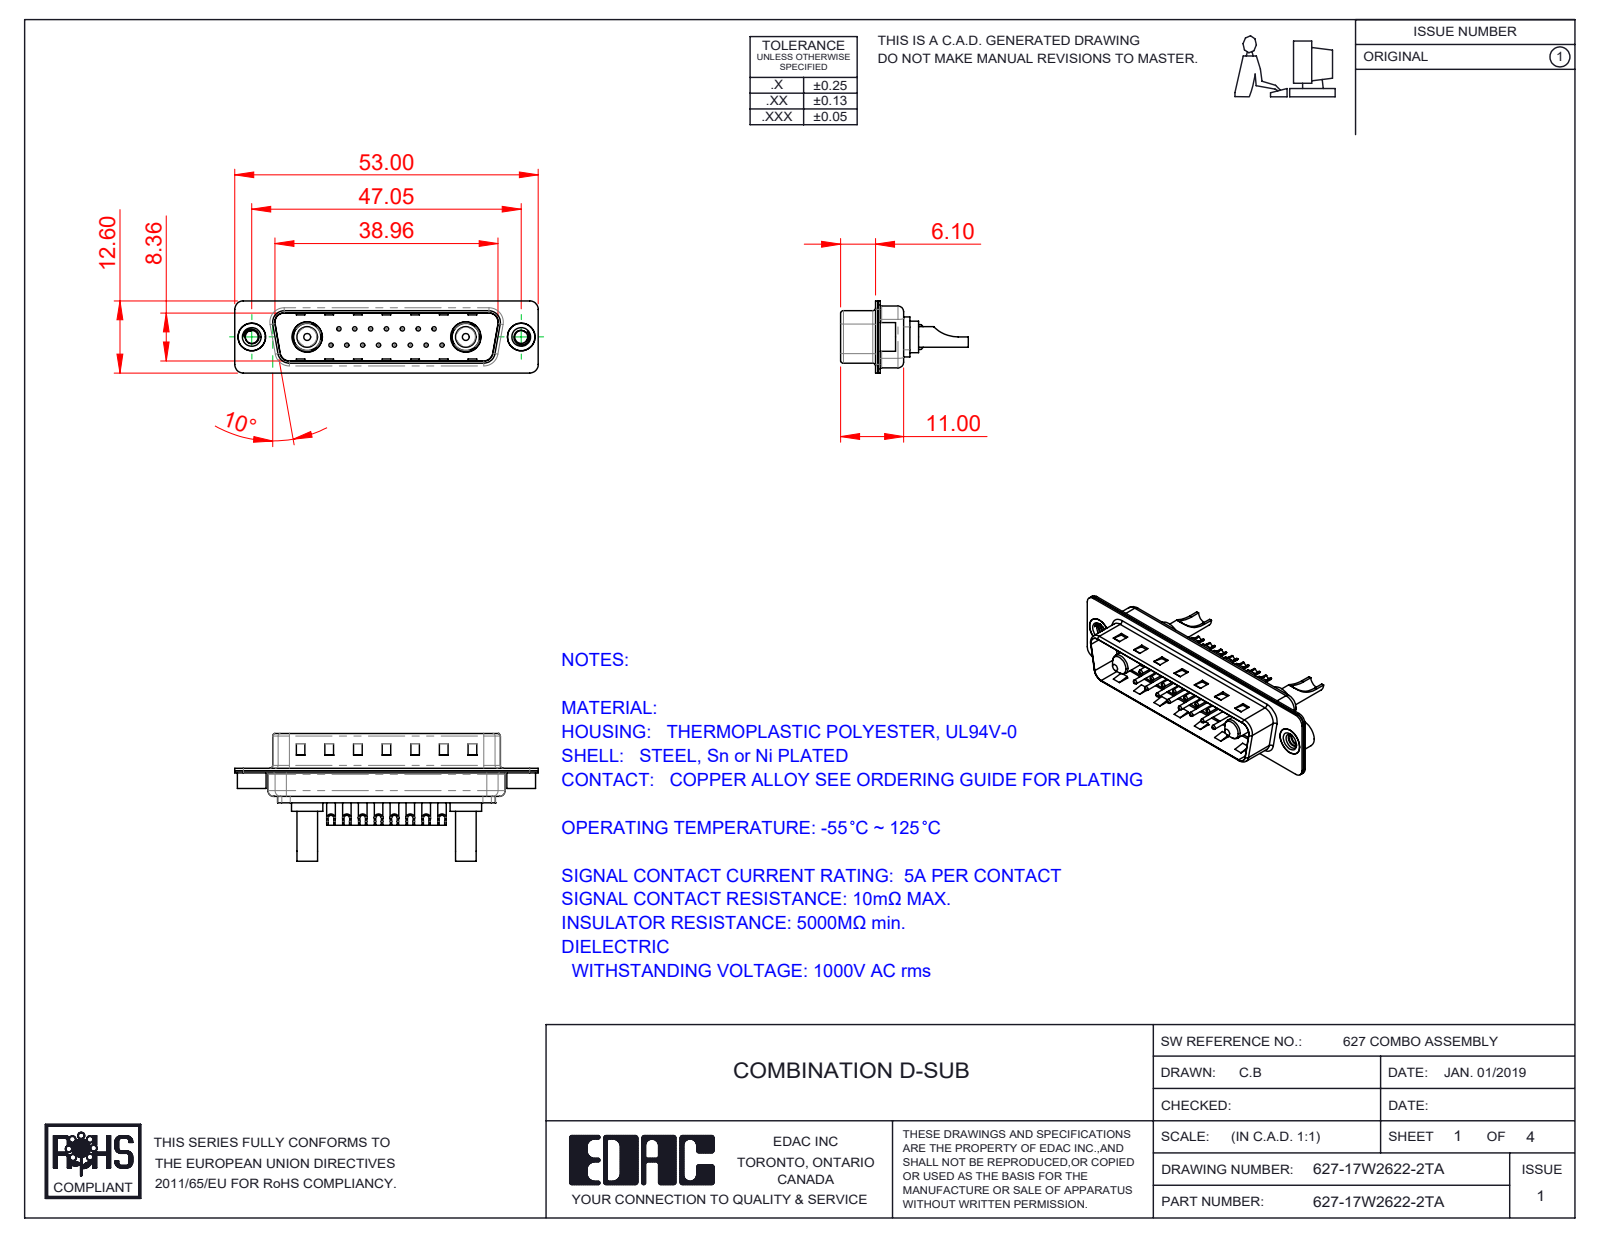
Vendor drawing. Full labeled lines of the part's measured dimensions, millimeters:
Part name (STEP PRODUCT): Power Pin_20A SC; 627Combo Housing_17W2; 627Combo Shell Front_25 Contacts; 627Combo Threaded Rivet_2 (+5 more)
STEP written by: SolidWorks 2016 (CONFIG_CONTROL_DESIGN)
Units: millimetres
Bodies: 24 solids, 1022 faces (332 planar, 422 cylindrical, 268 other)
Overall size (bounding box): 53 × 22.3 × 12.6
Volume: 2 906 mm³ · Surface area: 7 072 mm²
Round holes (diameter × count): ⌀0.75 ×15, ⌀1 ×15, ⌀1.6 ×15, ⌀2 ×15, ⌀2.26 ×2, ⌀2.7 ×2, ⌀4 ×2, ⌀4.8 ×2, ⌀4.85 ×2, ⌀5.3 ×2
Round bosses / shafts (diameter × count): ⌀1.5 ×15, ⌀5.5 ×2, ⌀5.2 ×2, ⌀5 ×2, ⌀4.9 ×2, ⌀4.75 ×2, ⌀3.75 ×2, ⌀3.6 ×2
Partial cylindrical surfaces — rounded edges, fillets, slot ends (radius × count): R1.5 ×16, R2 ×12, R0.5 ×8, R1.6 ×8, R1 ×6, R0.25 ×4, R0.6 ×4, R0.65 ×4
Main face-to-face distances: 0.4, 0.82, 9.58, 8.76, 1.5, 5.6, 5.2, 0.8, 1.22, 9.98
Hole centre spacings: 3.16, 2.77, 5.54, 8.31, 5.04, 7.49, 11.08, 5.03
